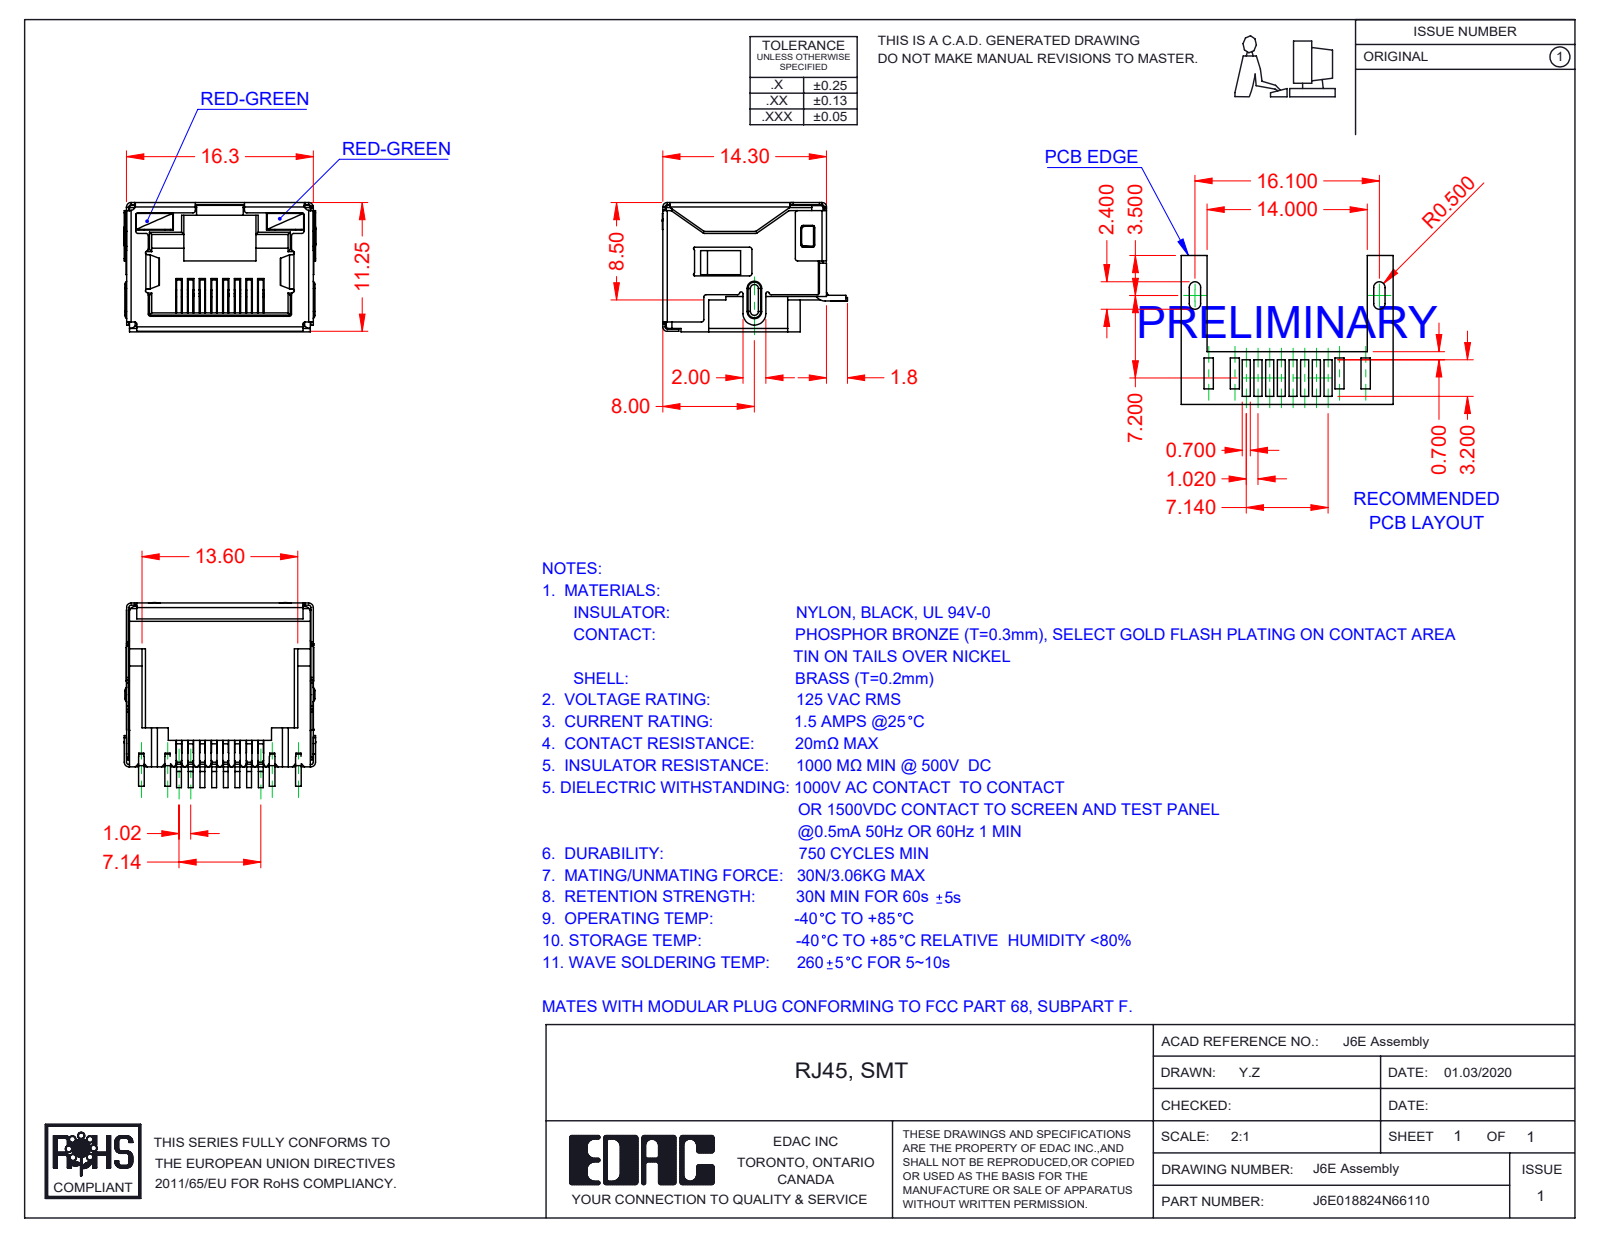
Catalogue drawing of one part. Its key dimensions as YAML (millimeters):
part_name: "6E Insulator_LED; 6E LED RH_6-Red-Green; 6E LED LH_6-Red-Green; 6E Contacts (+2 more)"
step_written_by: "SolidWorks 2016 (CONFIG_CONTROL_DESIGN)"
units: millimeters
bodies: {solids: 12, faces: 1500, planar: 1099, cylindrical: 351, other: 50}
overall_size: [16.75, 16.15, 11.3]
volume: 1109
surface_area: 4045
partial_cylinders:
  - {radius: 0.2, count: 82}
  - {radius: 0.25, count: 17}
  - {radius: 0.4, count: 13}
  - {radius: 0.5, count: 13}
  - {radius: 0.1, count: 10}
  - {radius: 0.15, count: 7}
  - {radius: 0.3, count: 4}
  - {radius: 1, count: 3}
face_to_face_distances: [11.05, 16.05, 16.1, 15.85, 11.1, 11.3, 2.4, 0.7, 9.85, 0.49]
